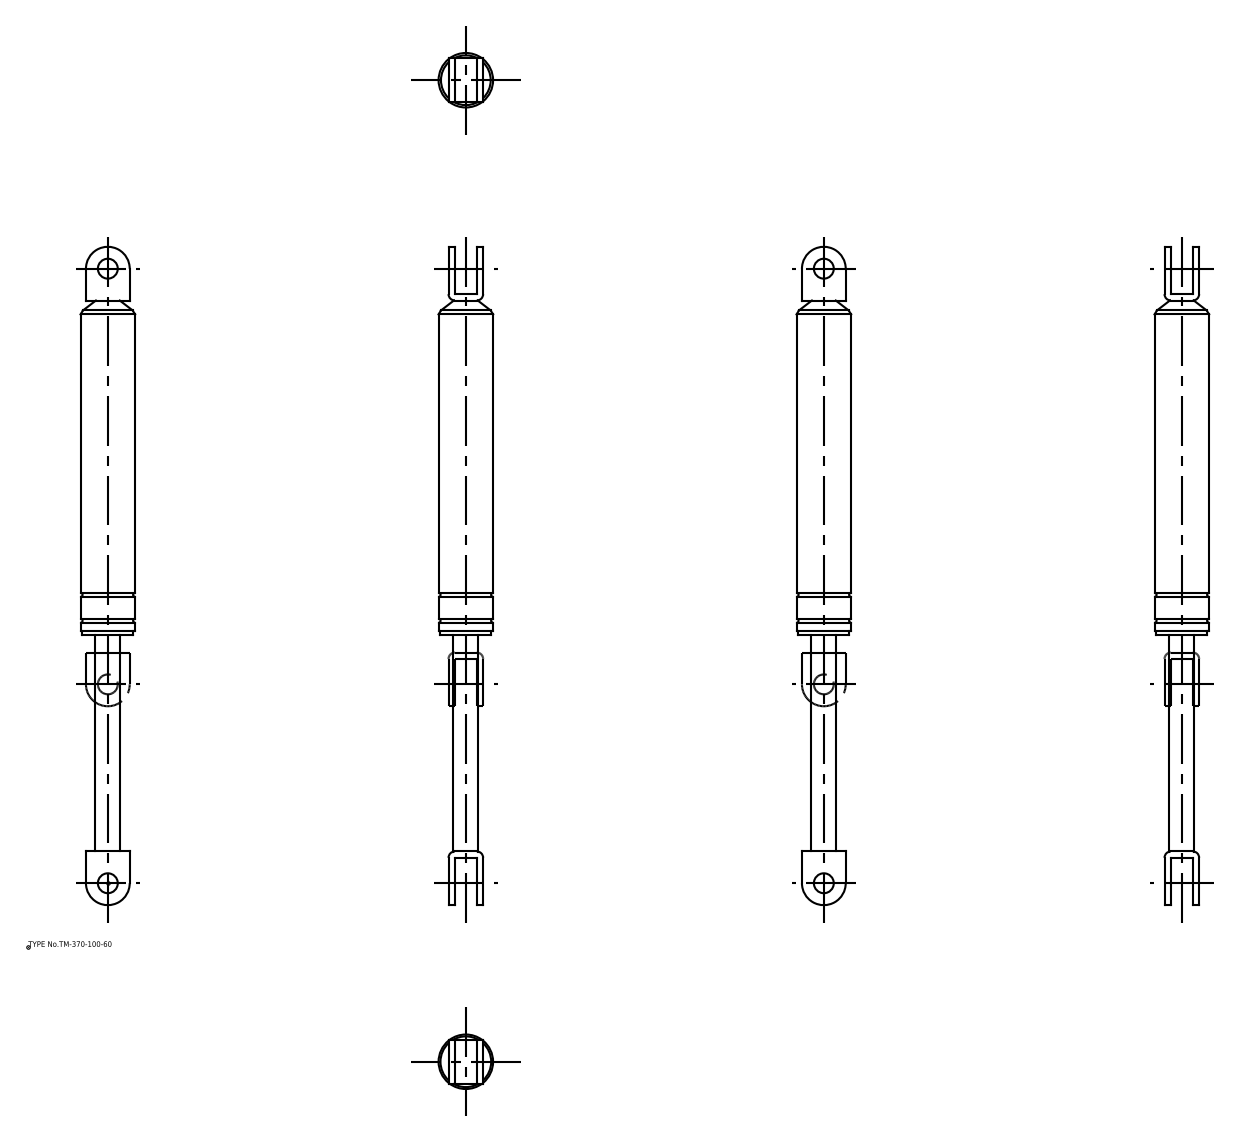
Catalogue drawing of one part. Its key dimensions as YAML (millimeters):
part_name: "TM_370_100_60; TM_370_100_60_div"
step_written_by: "spGate 16.7.1 (AUTOMOTIVE_DESIGN)"
units: millimeters
bodies: {solids: 2, faces: 64, planar: 22, cylindrical: 32, other: 10}
overall_size: [331, 28.2, 28.2]
volume: 118124
surface_area: 25523
round_holes:
  - {diameter: 10, count: 2}
round_bosses_or_shafts:
  - {diameter: 28.2, count: 1}
  - {diameter: 27.4, count: 1}
  - {diameter: 25.5, count: 1}
  - {diameter: 12.5, count: 1}
partial_cylinders:
  - {radius: 3.2, count: 4}
  - {radius: 11, count: 2}
face_to_face_distances: [3.2, 14.2, 17.4, 11, 22, 280.2, 112.2, 283.4, 171.2, 168]
hole_center_spacings: [309]
